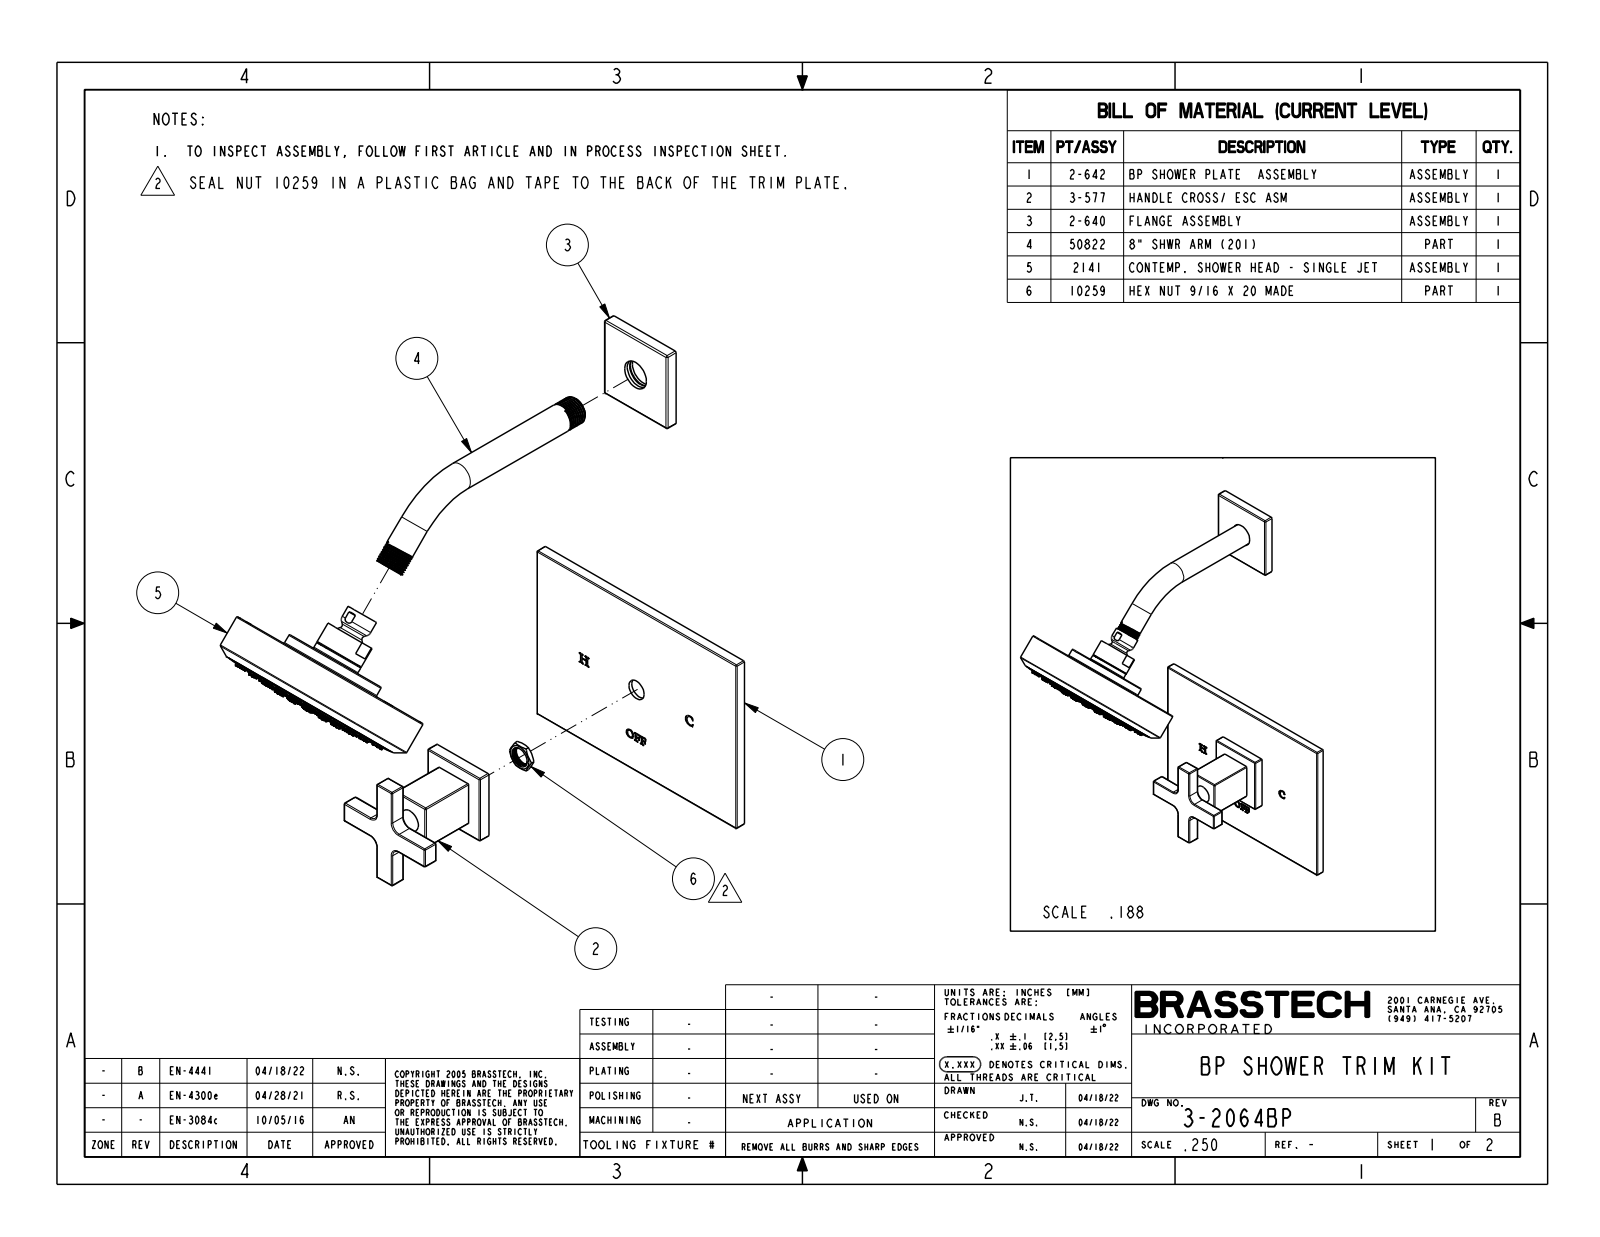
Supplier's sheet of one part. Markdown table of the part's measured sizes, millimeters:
| quantity | value |
| --- | --- |
| part name | 3-2064BP |
| STEP written by | CREO PARAMETRIC BY PTC INC, 2018400 (CONFIG_CONTROL_DESIGN) |
| units | millimeters |
| bodies | 2 solids, 1216 faces (181 planar, 278 cylindrical, 757 other) |
| overall size | 370.9 × 261.3 × 196.9 |
| volume | 963 900 mm³ |
| surface area | 152 000 mm² |
| round holes (diameter × count) | 1.3 × 90, 5.6 × 1, 133.5 × 1 |
| round bosses / shafts (diameter × count) | 35.6 × 2, 20.7 × 2, 150.1 × 1, 132.6 × 1, 74.2 × 1, 23 × 1, 16.5 × 1, 13.3 × 1 |
| partial cylindrical surfaces (radius × count) | 0.8 × 48, 1 × 8, 6.4 × 4 |
| main face-to-face distances | 7.9, 8.9, 1, 7.4, 85.2, 77.4, 76.4, 83.7, 113.2, 73.8 |
| hole center spacings | 24.9, 35.8, 10.9, 34.1, 37.6, 48.1, 12.4, 14 |
